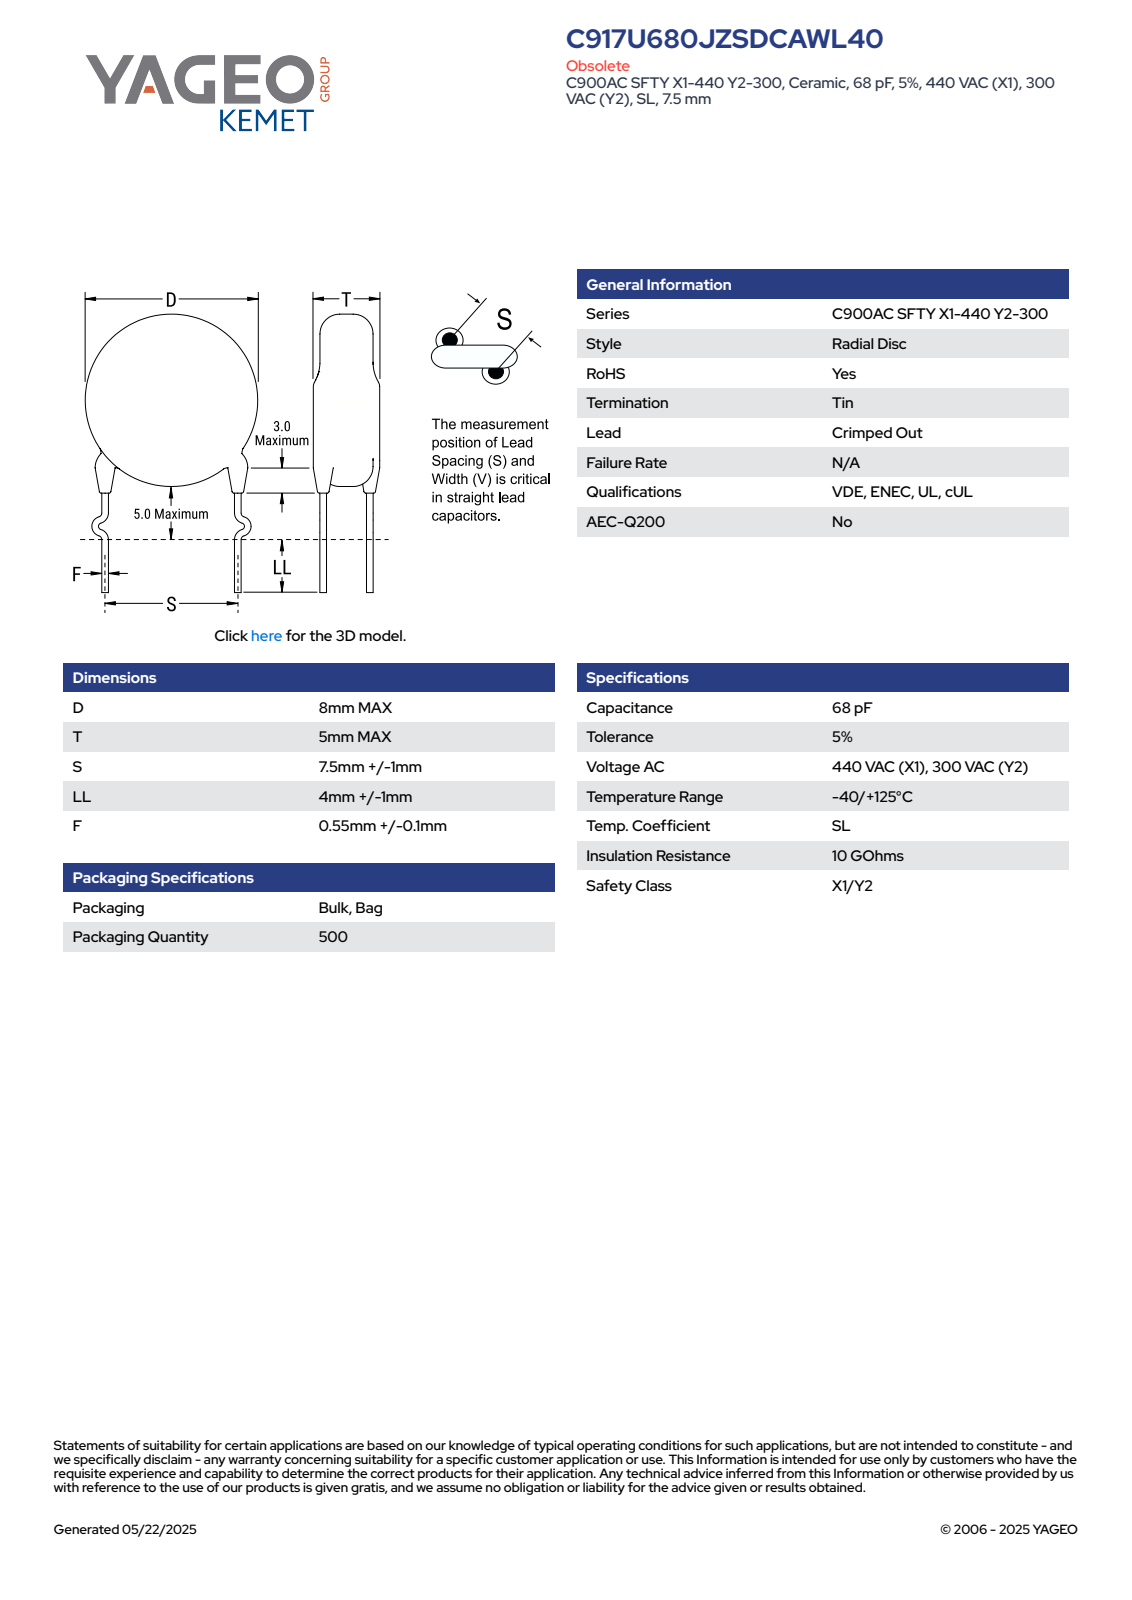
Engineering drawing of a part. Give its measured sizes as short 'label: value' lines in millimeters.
name: CCD_KCOC900_D8T5S7.5LL5F0.55
written by: SolidWorks 2014 (AUTOMOTIVE_DESIGN)
unit: mm
bodies: 4 solids, 87 faces (63 planar, 6 cylindrical, 18 other)
size: 18 × 12.09 × 5.04
volume: 254 mm³; area: 273 mm²
bosses: 2× ⌀1.2, 1× ⌀8
face distances: 5, 0.83, 4.42, 3.59, 3.39, 0.52, 0.31, 0.67, 1.71, 2.46
